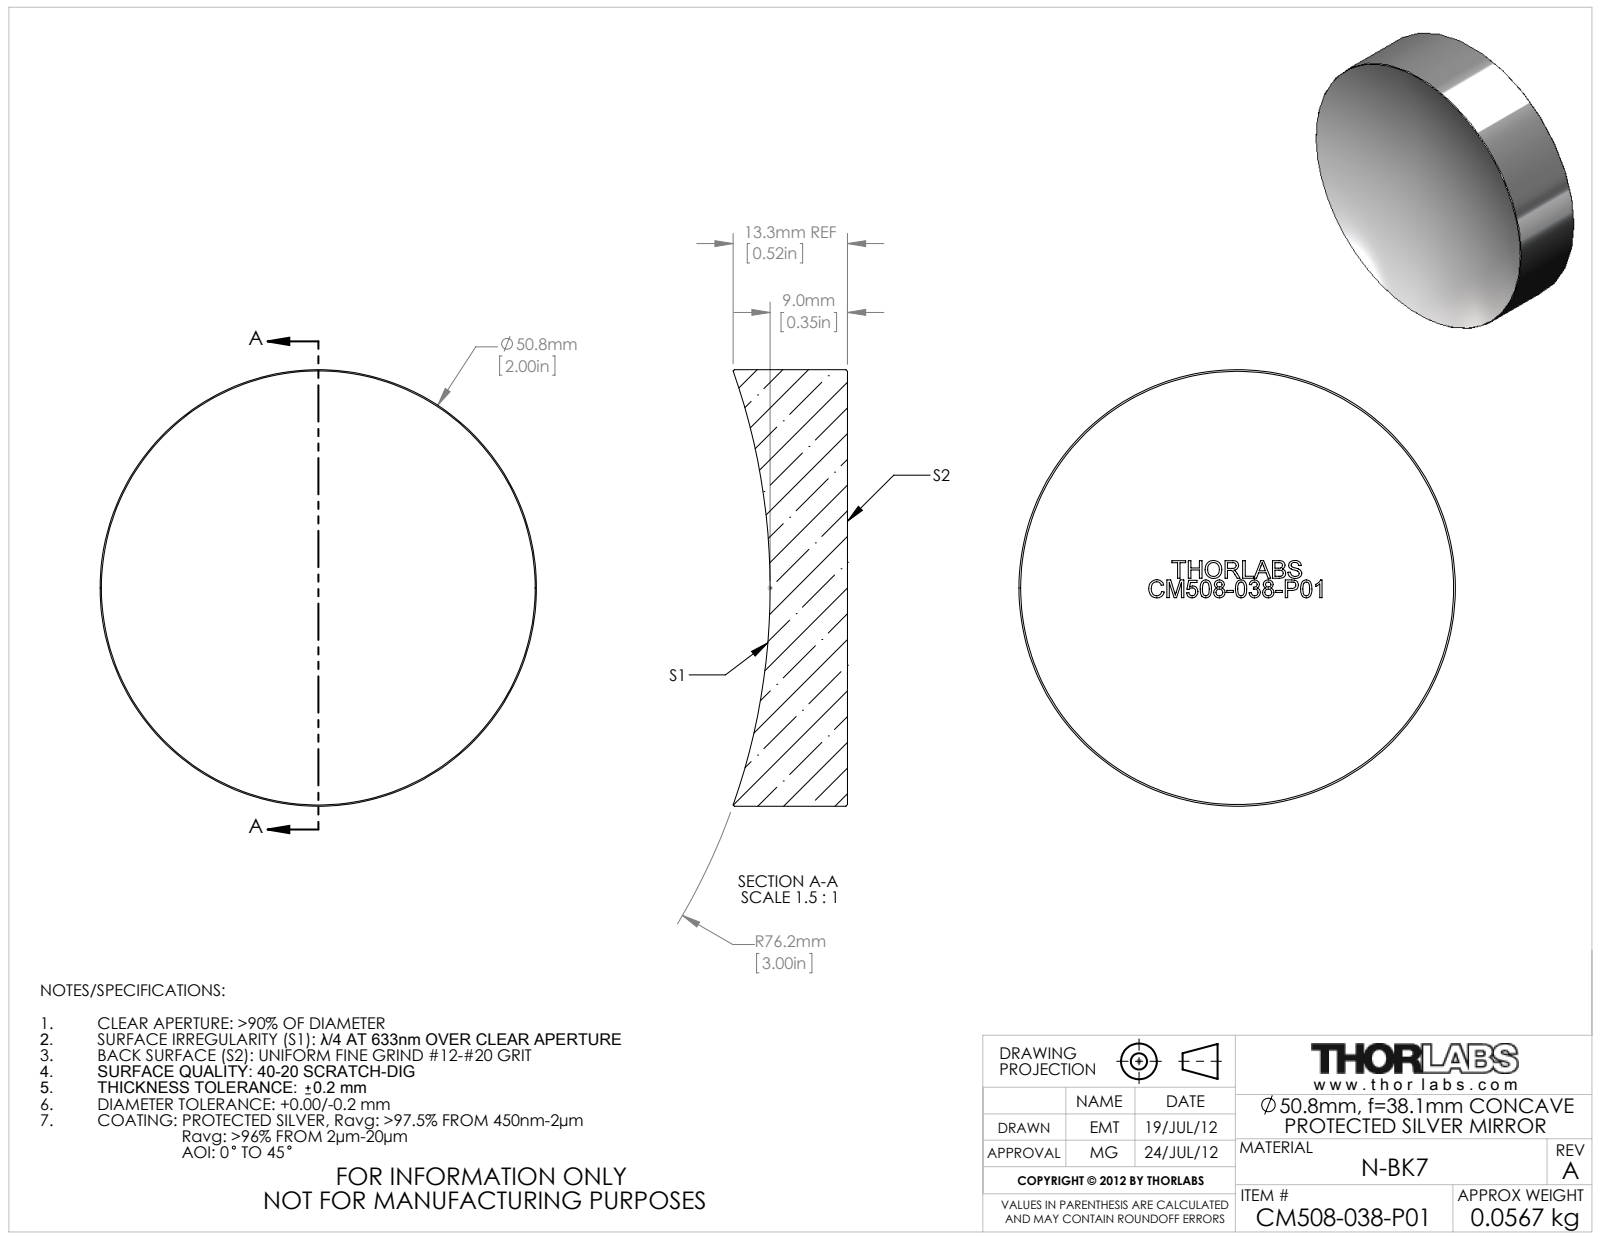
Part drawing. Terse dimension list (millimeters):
name: 24636-E0W
written by: SolidWorks 2011 (CONFIG_CONTROL_DESIGN)
unit: mm
bodies: 0 solids, 43 faces (35 planar, 2 cylindrical, 6 other)
size: 50.8 × 50.8 × 13.3
bosses: 1× ⌀50.8
